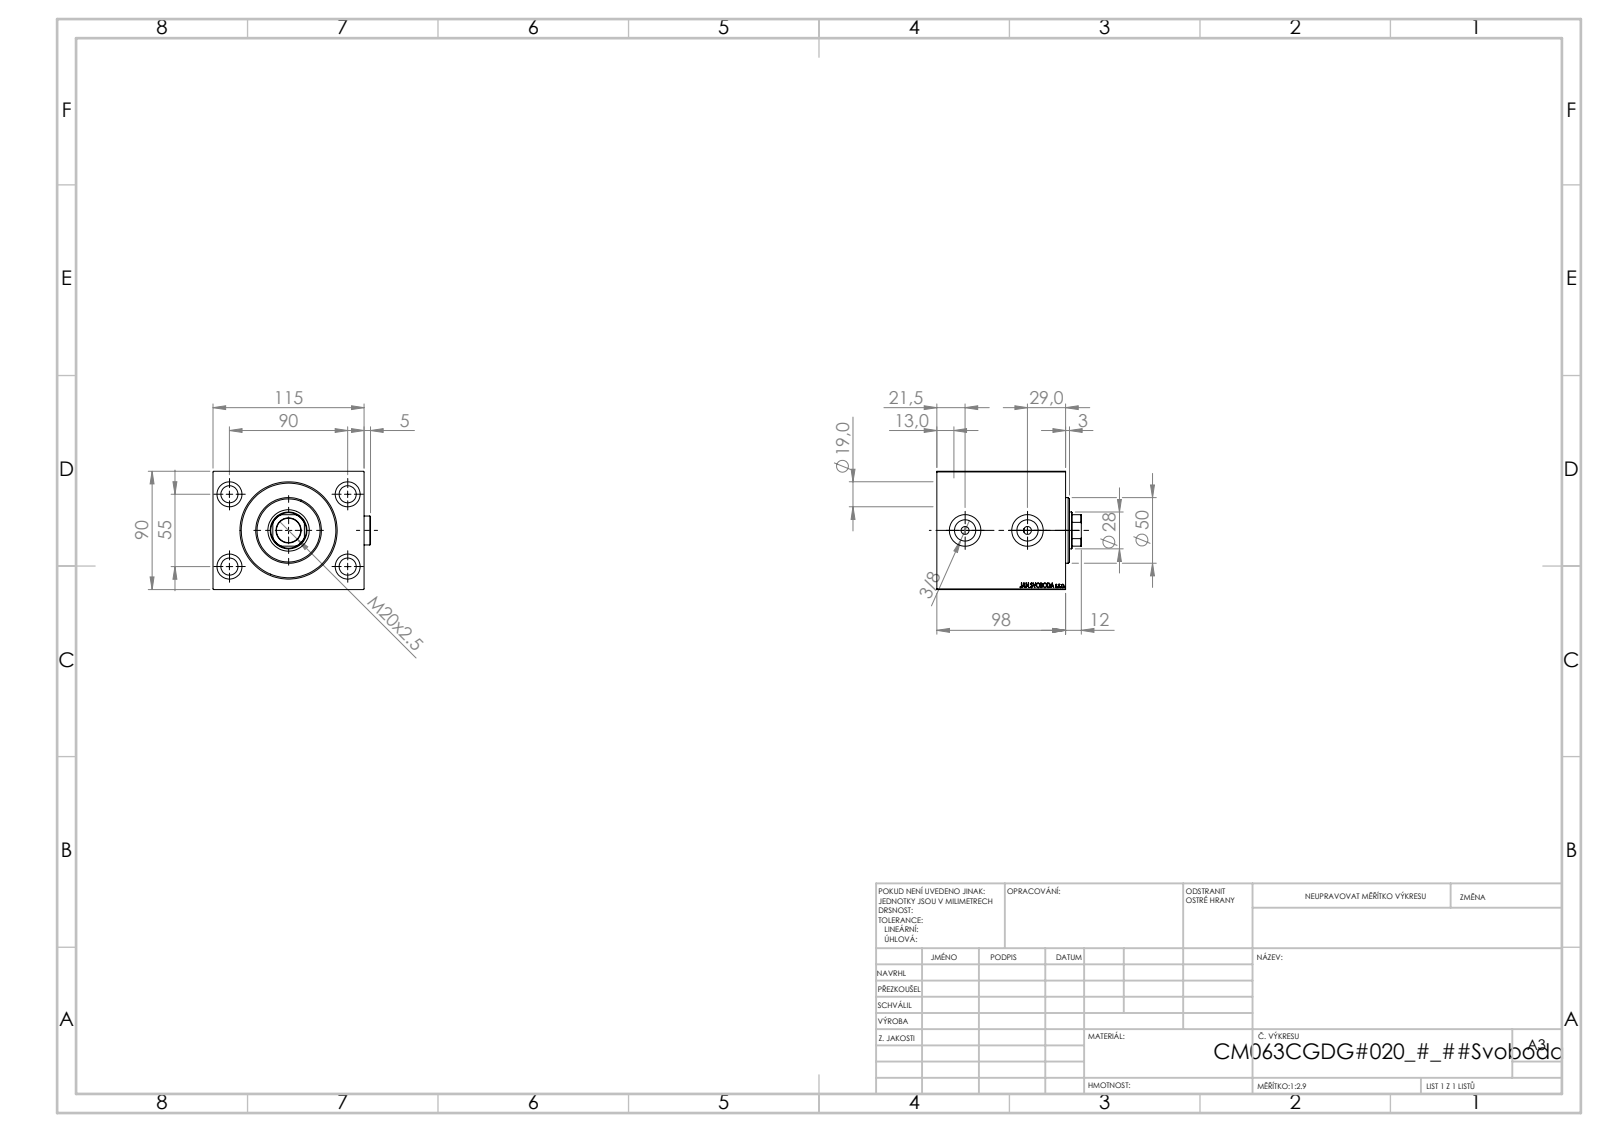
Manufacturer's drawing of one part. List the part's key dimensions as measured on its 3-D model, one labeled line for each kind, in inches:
Part name (STEP PRODUCT): V450CM_VC_B; V450CM_C_Body; Zatka_OIL_PORT; V450CM_C_VCP
STEP written by: SolidWorks 2019 (CONFIG_CONTROL_DESIGN)
Units: inches
Bodies: 5 solids, 917 faces (443 planar, 76 cylindrical, 398 other)
Overall size (bounding box): 4.72 × 4.331 × 3.543
Volume: 55.77 in³ · Surface area: 192.7 in²
Round holes (diameter × count): ⌀0.512 ×4, ⌀0.748 ×4, ⌀0.236 ×2, ⌀0.637 ×2, ⌀0.945 ×2, ⌀0.728 ×1, ⌀1.102 ×1, ⌀1.24 ×1, ⌀2.48 ×1, ⌀2.559 ×1, ⌀2.835 ×1
Round bosses / shafts (diameter × count): ⌀0.866 ×2, ⌀1.969 ×1
Partial cylindrical surfaces — rounded edges, fillets, slot ends (radius × count): R0.531 ×1
Main face-to-face distances: 3.543, 4.528, 3.858, 2.008, 1.85, 0.85, 1.157, 3.008, 0.394, 1.244
Hole centre spacings: 2.076, 2.165, 3.543, 4.153, 1.87
